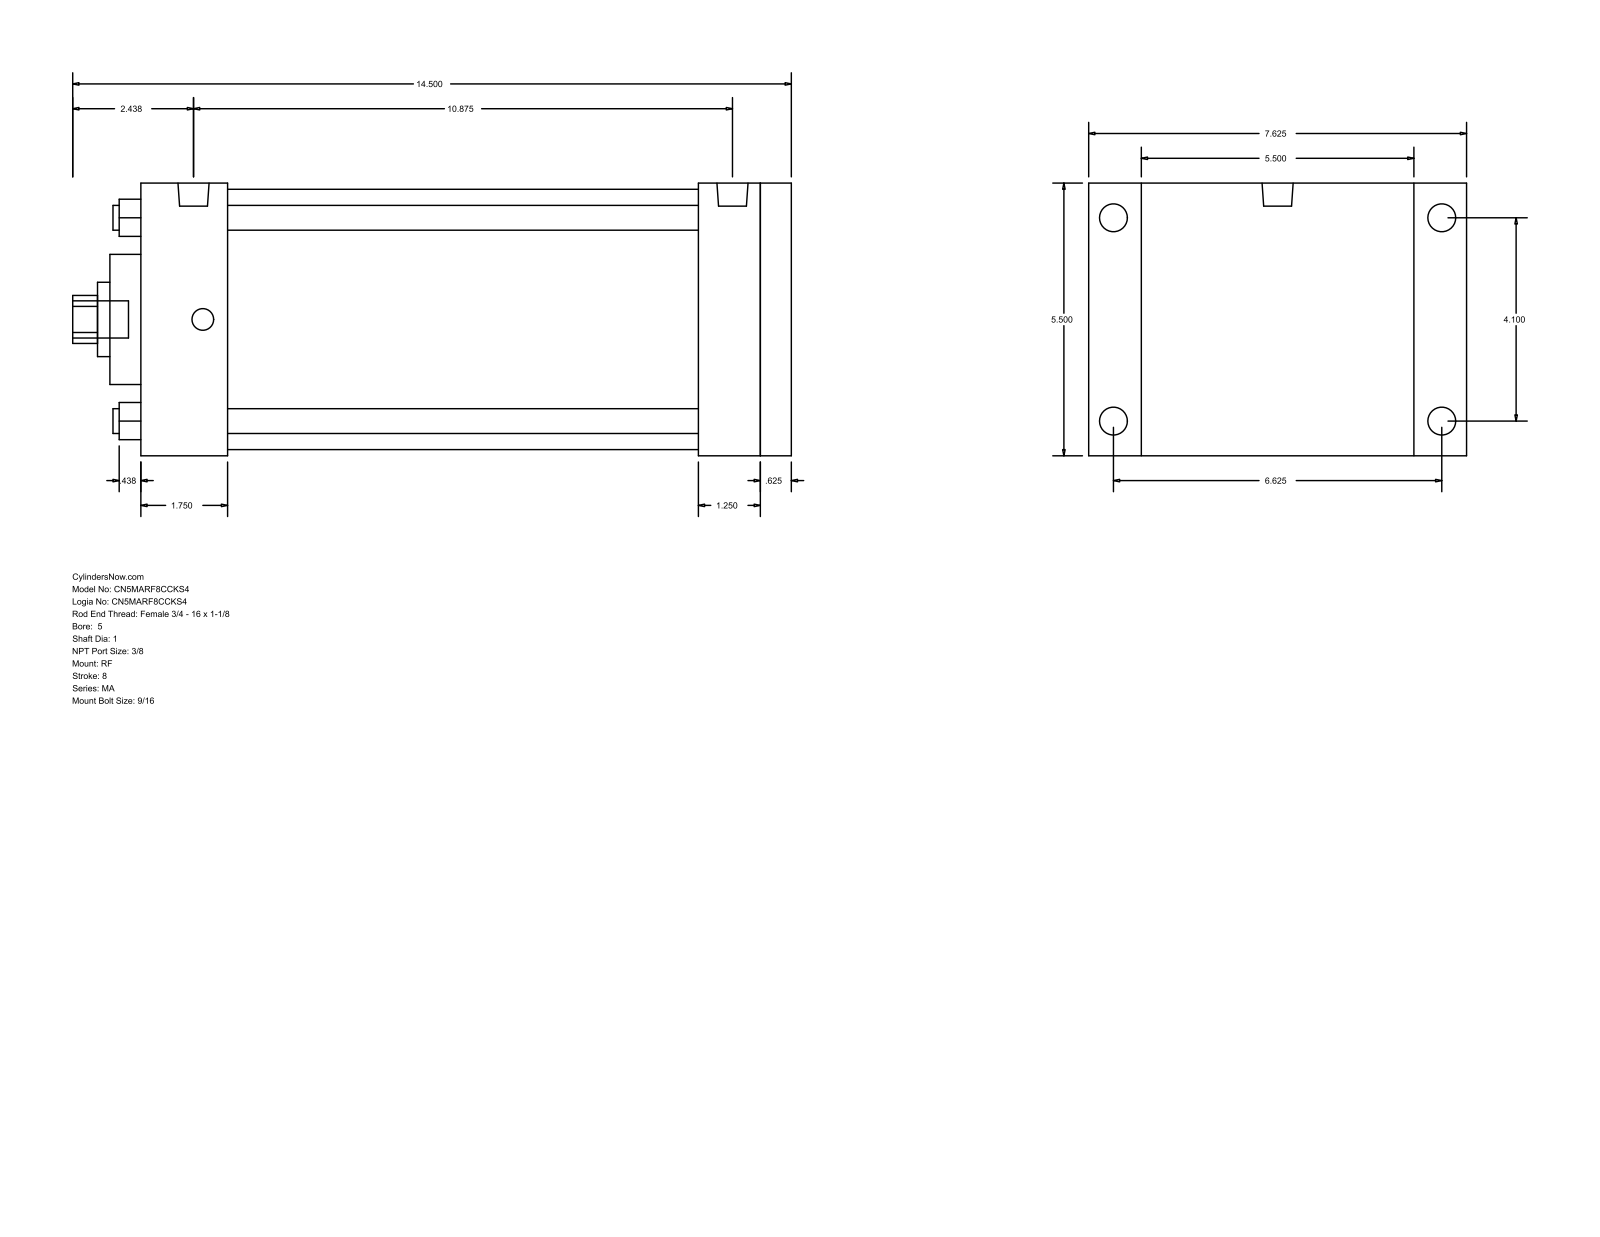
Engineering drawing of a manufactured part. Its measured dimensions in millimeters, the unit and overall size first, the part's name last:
Units: millimetres
Overall size (bounding box): 368.3 × 193.68 × 139.7
Round holes (diameter × count): ⌀12.7 ×4, ⌀25.4 ×1, ⌀38.1 ×1, ⌀66.67 ×1, ⌀133.35 ×1
Round bosses / shafts (diameter × count): ⌀14.29 ×4, ⌀11.11 ×4, ⌀15.93 ×2, ⌀19.05 ×1
Partial cylindrical surfaces — rounded edges, fillets, slot ends (radius × count): R12.29 ×1
Main face-to-face distances: 139.7, 333.38, 15.87, 317.51, 44.46, 273.05, 288.92, 285.76, 241.3, 31.75
Hole centre spacings: 73.64, 104.14, 147.28
Bodies: 0 solids, 94 faces (65 planar, 29 cylindrical, 0 other)
Part name (STEP PRODUCT): MA_RF__0500_1
STEP written by: GSSL Pune (CONFIG_CONTROL_DESIGN)
